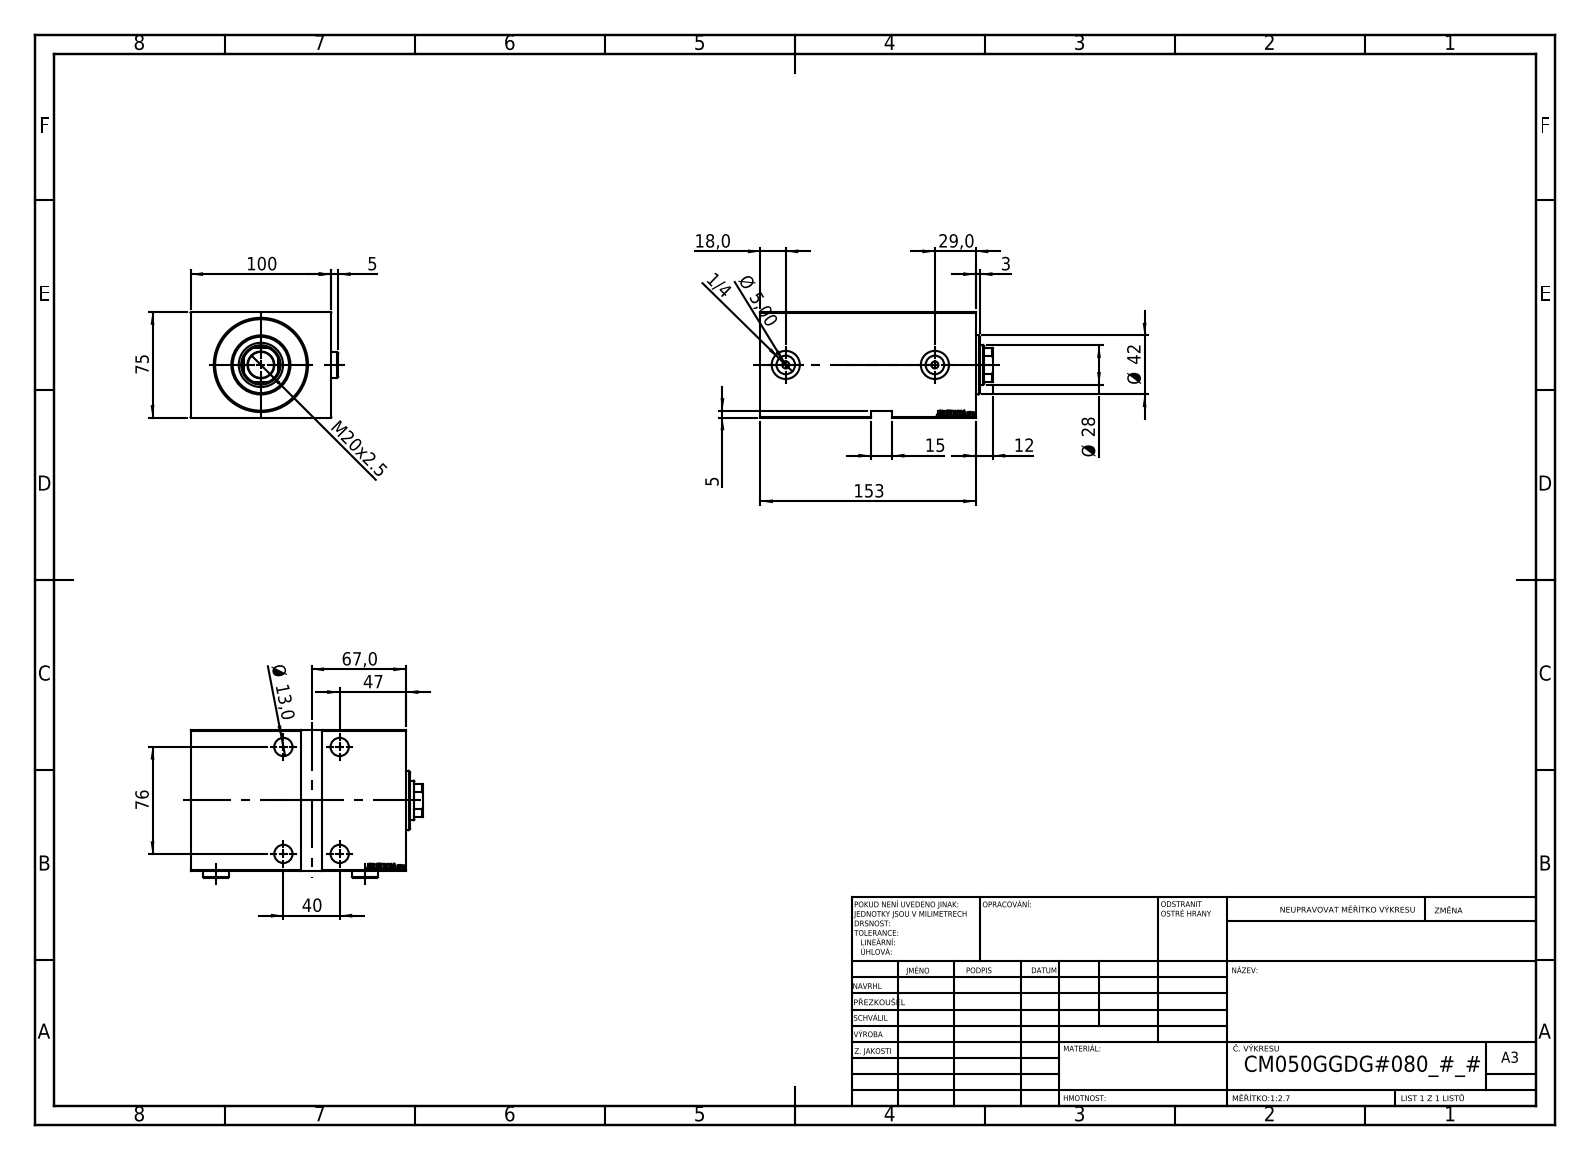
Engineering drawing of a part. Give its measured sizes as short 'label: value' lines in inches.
name: V450CM_G_VCP; V450CM_G_Body; V450CM_VC_G; Zatka_OIL_PORT
written by: SolidWorks 2019 (CONFIG_CONTROL_DESIGN)
unit: in
bodies: 5 solids, 912 faces (446 planar, 68 cylindrical, 398 other)
size: 6.496 × 4.13 × 2.953
volume: 58.86 in³; area: 213.9 in²
holes: 4× ⌀0.512, 4× ⌀0.748, 2× ⌀0.197, 2× ⌀0.518, 2× ⌀0.787, 1× ⌀0.728, 1× ⌀1.102, 1× ⌀1.24, 1× ⌀1.969, 1× ⌀2.047, 1× ⌀2.559
bosses: 2× ⌀0.709, 1× ⌀1.654
rounds: 1× R0.531
face distances: 2.953, 3.937, 6.024, 0.197, 0.551, 5.472, 5.827, 5.276, 3.425, 2.756
hole spacings: 1.575, 2.992, 3.381, 4.173
